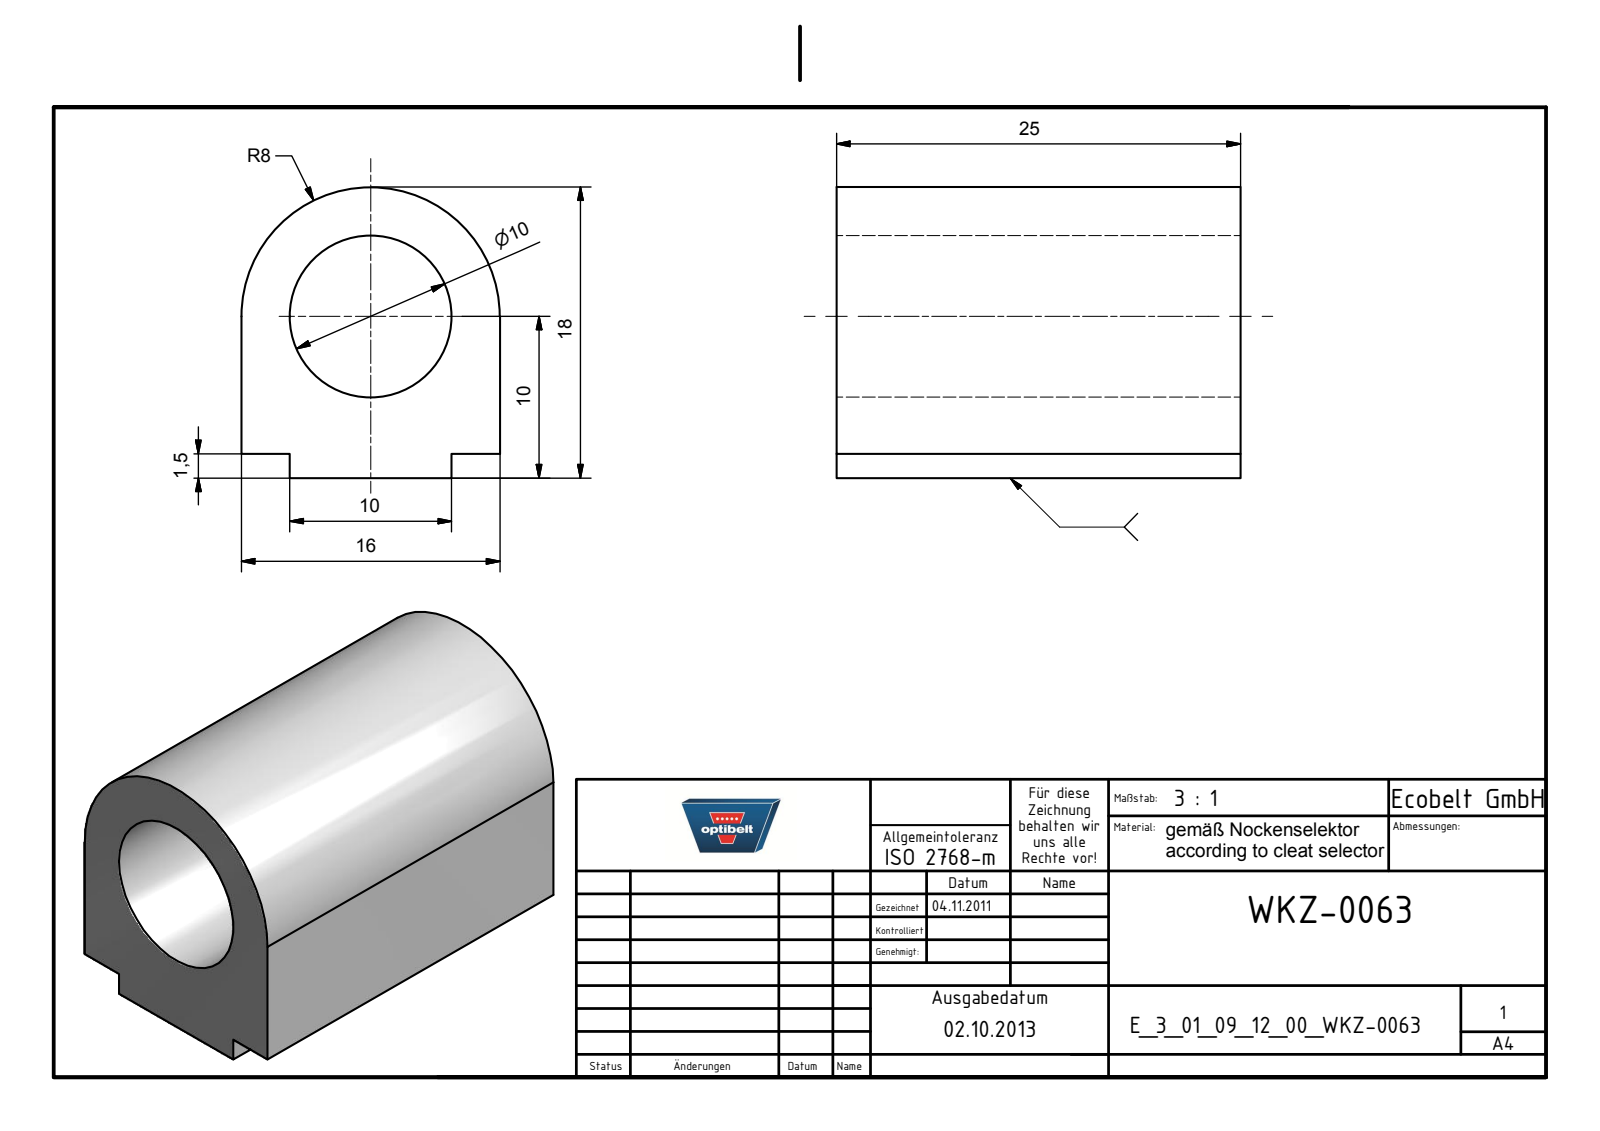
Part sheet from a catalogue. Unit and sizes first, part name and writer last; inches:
Units: inches
Overall size (bounding box): 0.984 × 0.709 × 0.63
Round holes (diameter × count): ⌀0.394 ×1
Partial cylindrical surfaces — rounded edges, fillets, slot ends (radius × count): R0.315 ×1
Main face-to-face distances: 0.63, 0.984, 0.059, 0.118, 0.512, 0.394
Volume: 0.264 in³ · Surface area: 4.123 in²
Bodies: 1 solid, 11 faces (9 planar, 2 cylindrical, 0 other)
Part name (STEP PRODUCT): E_3_01_09_12_00_WKZ-0063
STEP written by: Autodesk Inventor 2013 (AUTOMOTIVE_DESIGN)
